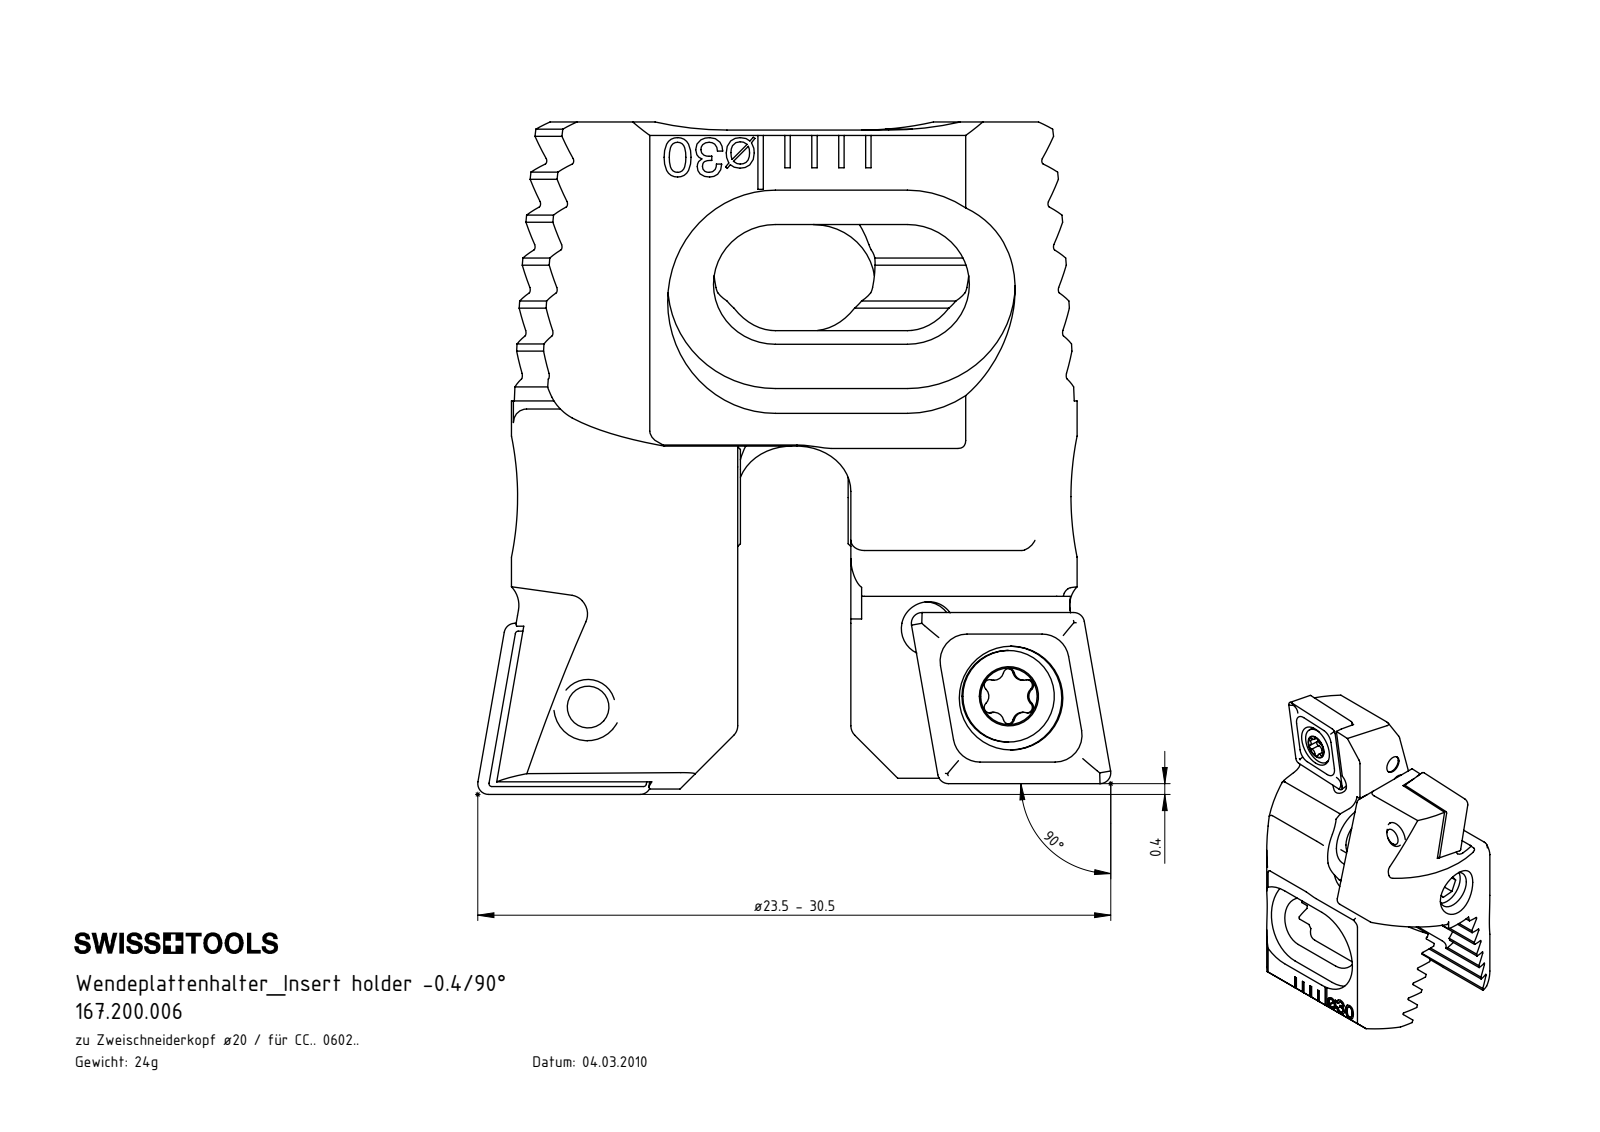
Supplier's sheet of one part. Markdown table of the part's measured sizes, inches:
| quantity | value |
| --- | --- |
| part name | WCA-ER2.001.006_A; Z20-xxx.001.015_D; CCMT060204; Z20-ER3.001.018_A (+5 more) |
| STEP written by | SolidWorks 2022 (AUTOMOTIVE_DESIGN) |
| units | inches |
| bodies | 11 solids, 677 faces (282 planar, 159 cylindrical, 236 other) |
| overall size | 0.982 × 0.886 × 0.638 |
| volume | 0.192 in³ |
| surface area | 5.884 in² |
| round holes (diameter × count) | 0.063 × 4, 0.098 × 3, 0.079 × 2, 0.081 × 2, 0.11 × 2, 0.152 × 2, 0.138 × 1, 0.358 × 1 |
| round bosses / shafts (diameter × count) | 0.118 × 4, 0.134 × 2, 0.098 × 2, 0.346 × 1, 0.157 × 1 |
| partial cylindrical surfaces (radius × count) | 0.02 × 16, 0.005 × 12, 0.008 × 12, 0.014 × 8, 0.014 × 4, 0.079 × 4, 0.091 × 4, 0.157 × 4 |
| main face-to-face distances | 0.056, 0.113, 0.169, 0.016, 0.149, 0.225, 0.225, 0.142, 0.157, 0.117 |
| hole center spacings | 0.098, 0.154, 0.158, 0.217, 0.197, 0.238, 0.293, 0.351 |
